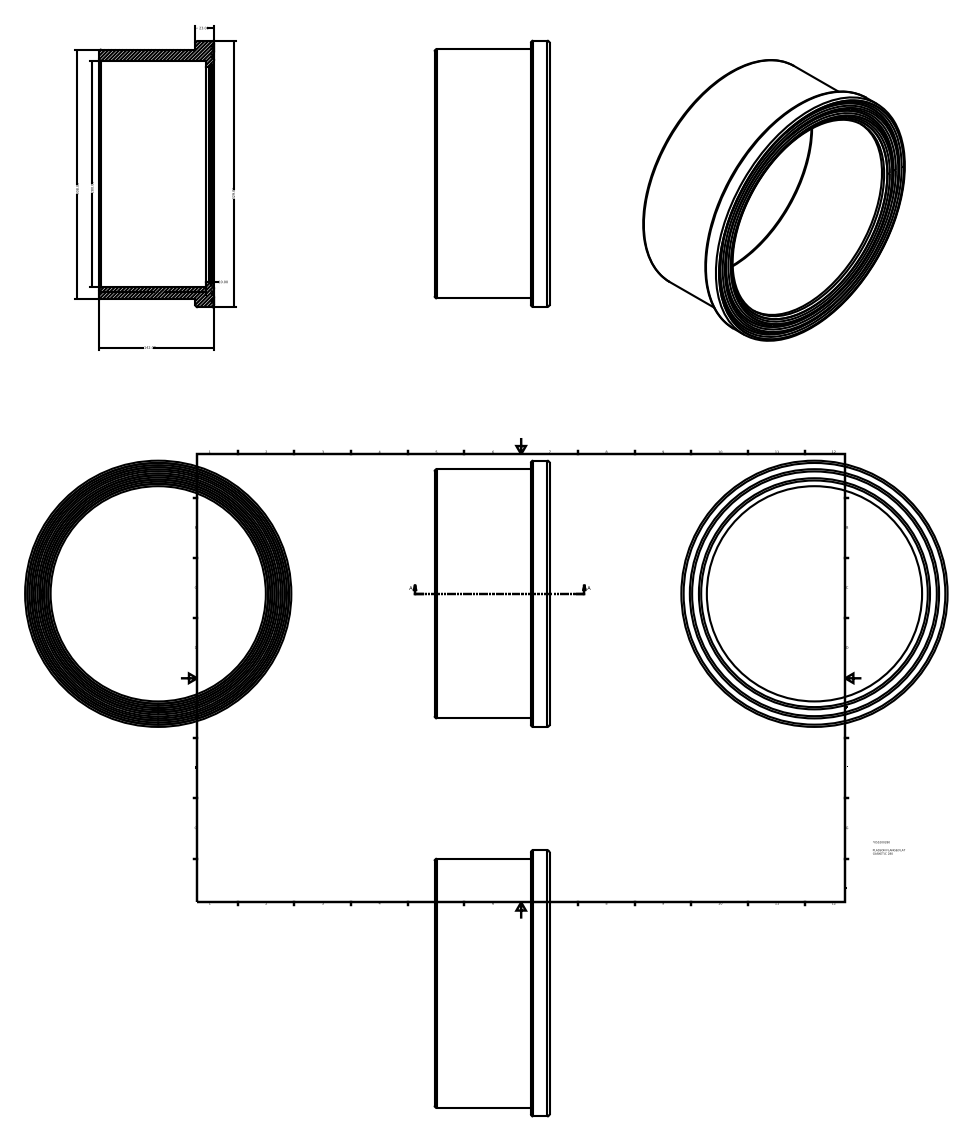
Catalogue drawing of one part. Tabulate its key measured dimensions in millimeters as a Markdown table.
| quantity | value |
| --- | --- |
| part name | (_AS)055200280 |
| STEP written by | Autodesk Inventor 2015 (AUTOMOTIVE_DESIGN) |
| units | millimeters |
| bodies | 1 solid, 27 faces (8 planar, 4 cylindrical, 15 other) |
| overall size | 329 × 329 × 142 |
| volume | 2 079 000 mm³ |
| surface area | 320 325 mm² |
| round holes (diameter × count) | 266 × 1, 280 × 1 |
| round bosses / shafts (diameter × count) | 329 × 1, 308 × 1 |
| main face-to-face distances | 119, 132, 13, 138.55, 19.55, 6.55, 142, 23, 10, 3.45 |
